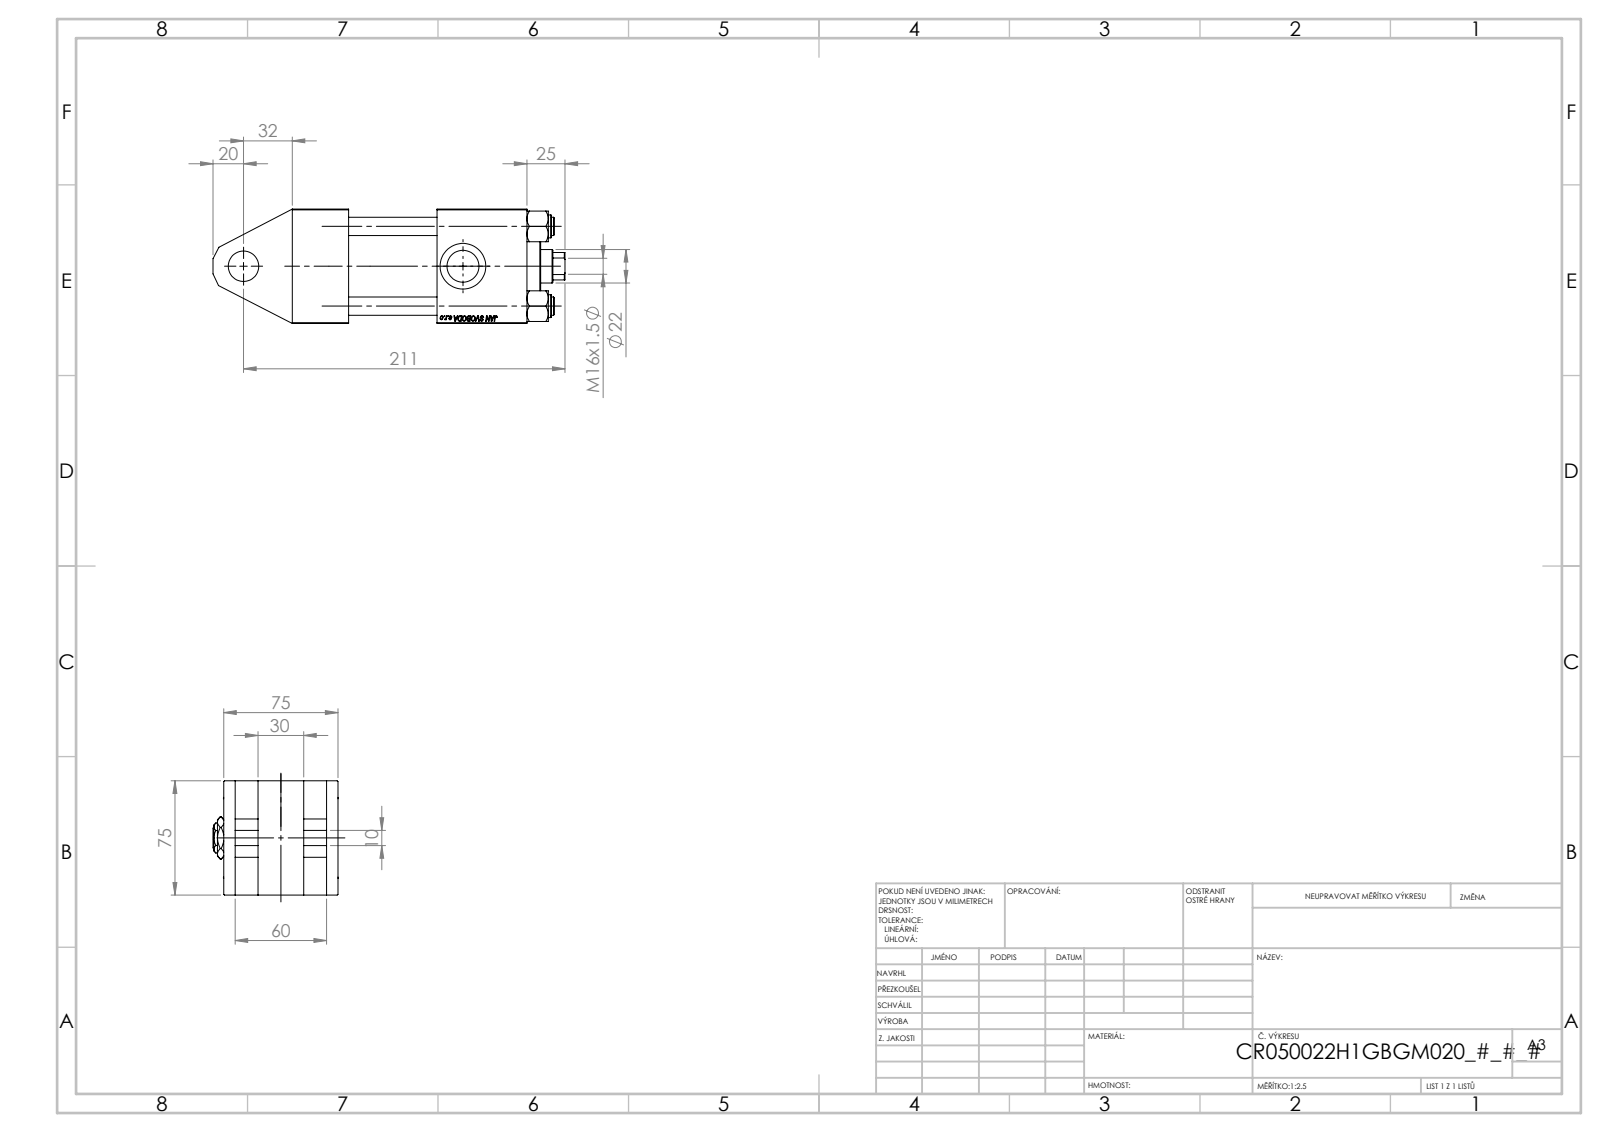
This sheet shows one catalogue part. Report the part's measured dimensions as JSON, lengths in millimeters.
{"part_name": "NUT_M5_H; V215CR_H_Body; V215CR_VCP_H; V215CR_TYCINKA_H (+2 more)", "step_written_by": "SolidWorks 2019 (CONFIG_CONTROL_DESIGN)", "units": "millimeters", "bodies": {"solids": 12, "faces": 1176, "planar": 541, "cylindrical": 87, "other": 548}, "overall_size": [231, 82.27, 75], "volume_mm3": 730706, "surface_area_mm2": 164844, "round_holes": [[12, 4], [7, 2], [20.96, 2], [30, 2], [10.5, 1], [20, 1], [22, 1], [25, 1], [41, 1], [50, 1], [53, 1]], "round_bosses_or_shafts": [[15, 4], [56, 1], [34, 1]], "partial_cylinders_radius": [[10.5, 1]], "face_to_face_distances": [75, 117, 67.5, 7.5, 45, 22.5, 52.5, 15, 95, 37], "hole_center_spacings": [36.98, 52.3, 73.96, 50.5, 93.5, 144]}
